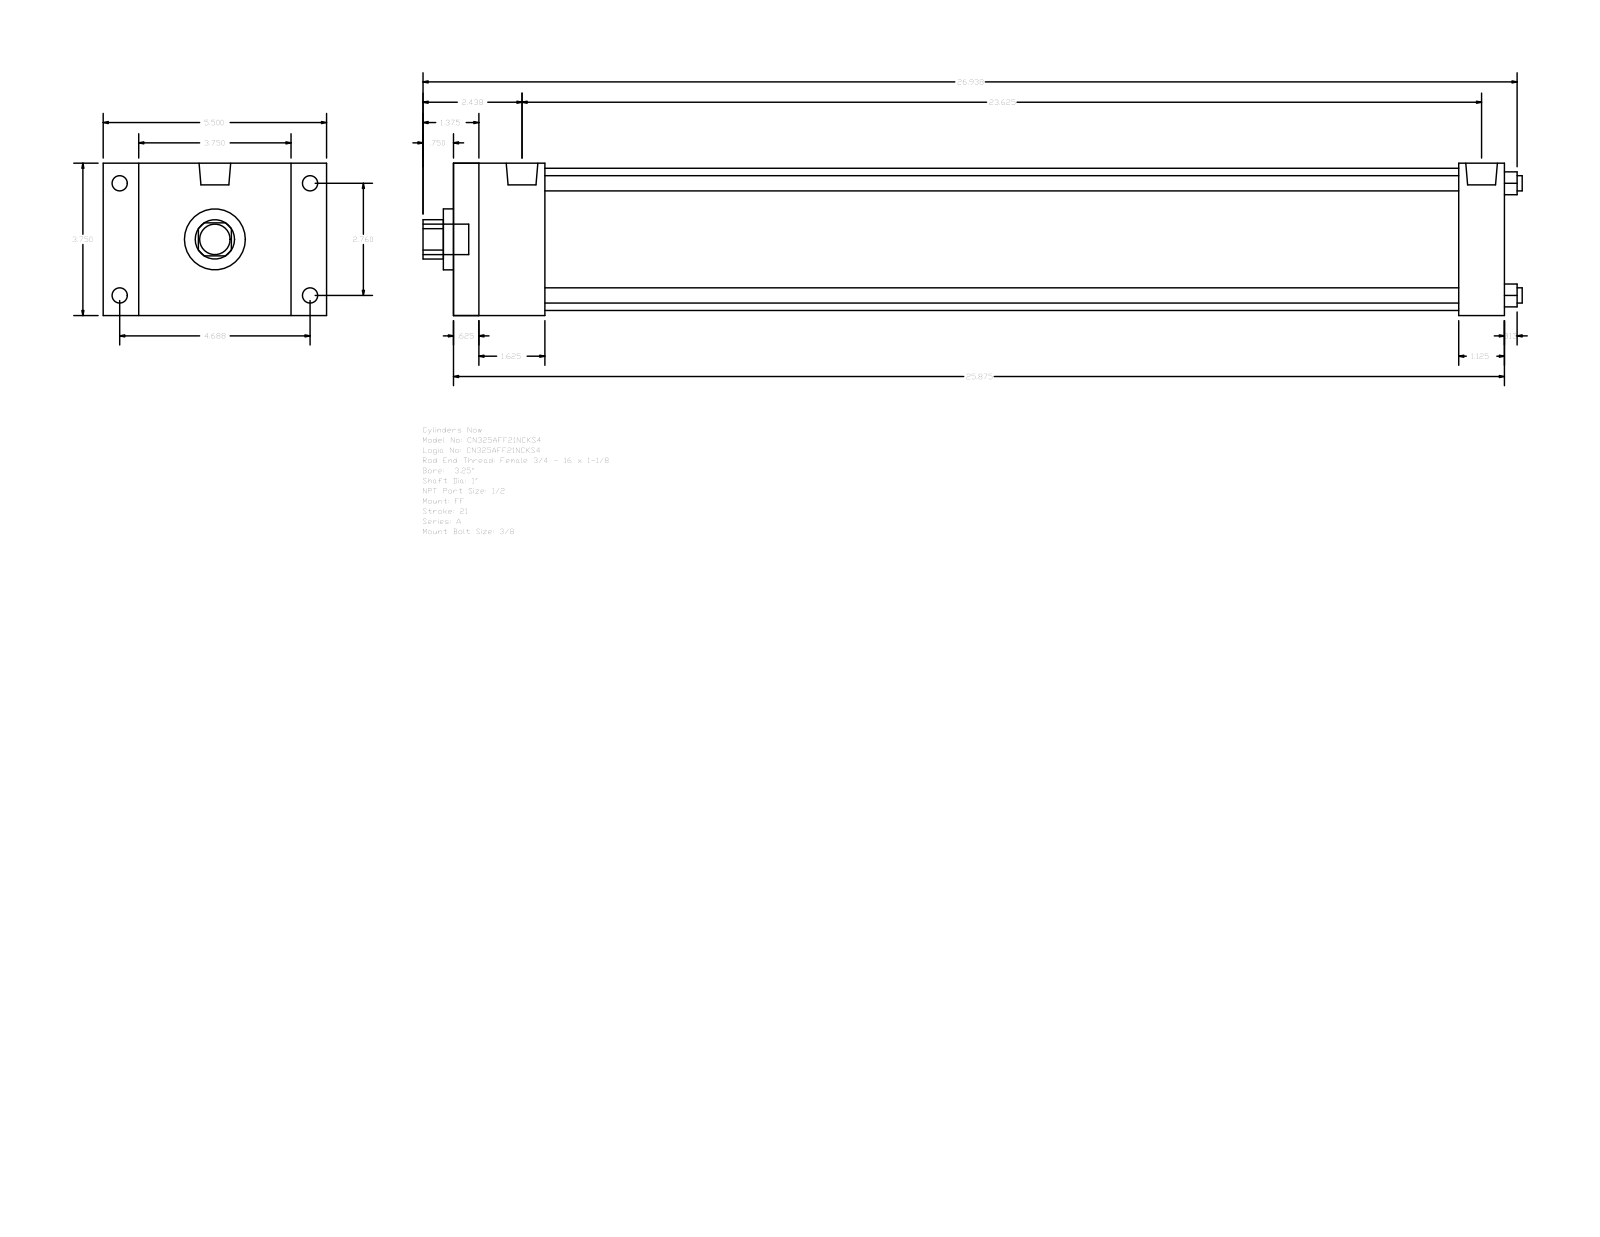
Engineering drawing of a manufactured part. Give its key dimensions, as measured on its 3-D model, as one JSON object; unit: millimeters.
{"part_name": "A_FF__0325_1", "step_written_by": "GSSL Pune (CONFIG_CONTROL_DESIGN)", "units": "millimeters", "bodies": {"solids": 0, "faces": 92, "planar": 64, "cylindrical": 28, "other": 0}, "overall_size": [687.39, 139.7, 95.25], "round_holes": [[9.53, 4], [25.4, 1], [38.1, 1], [88.9, 1]], "round_bosses_or_shafts": [[9.53, 4], [8.73, 4], [19.77, 2], [19.05, 1]], "partial_cylinders_radius": [[12.29, 1]], "face_to_face_distances": [95.24, 657.22, 15.87, 641.35, 22.23, 117.47, 28.57, 57.15, 628.65, 41.28], "hole_center_spacings": [49.57, 70.1, 99.14]}
